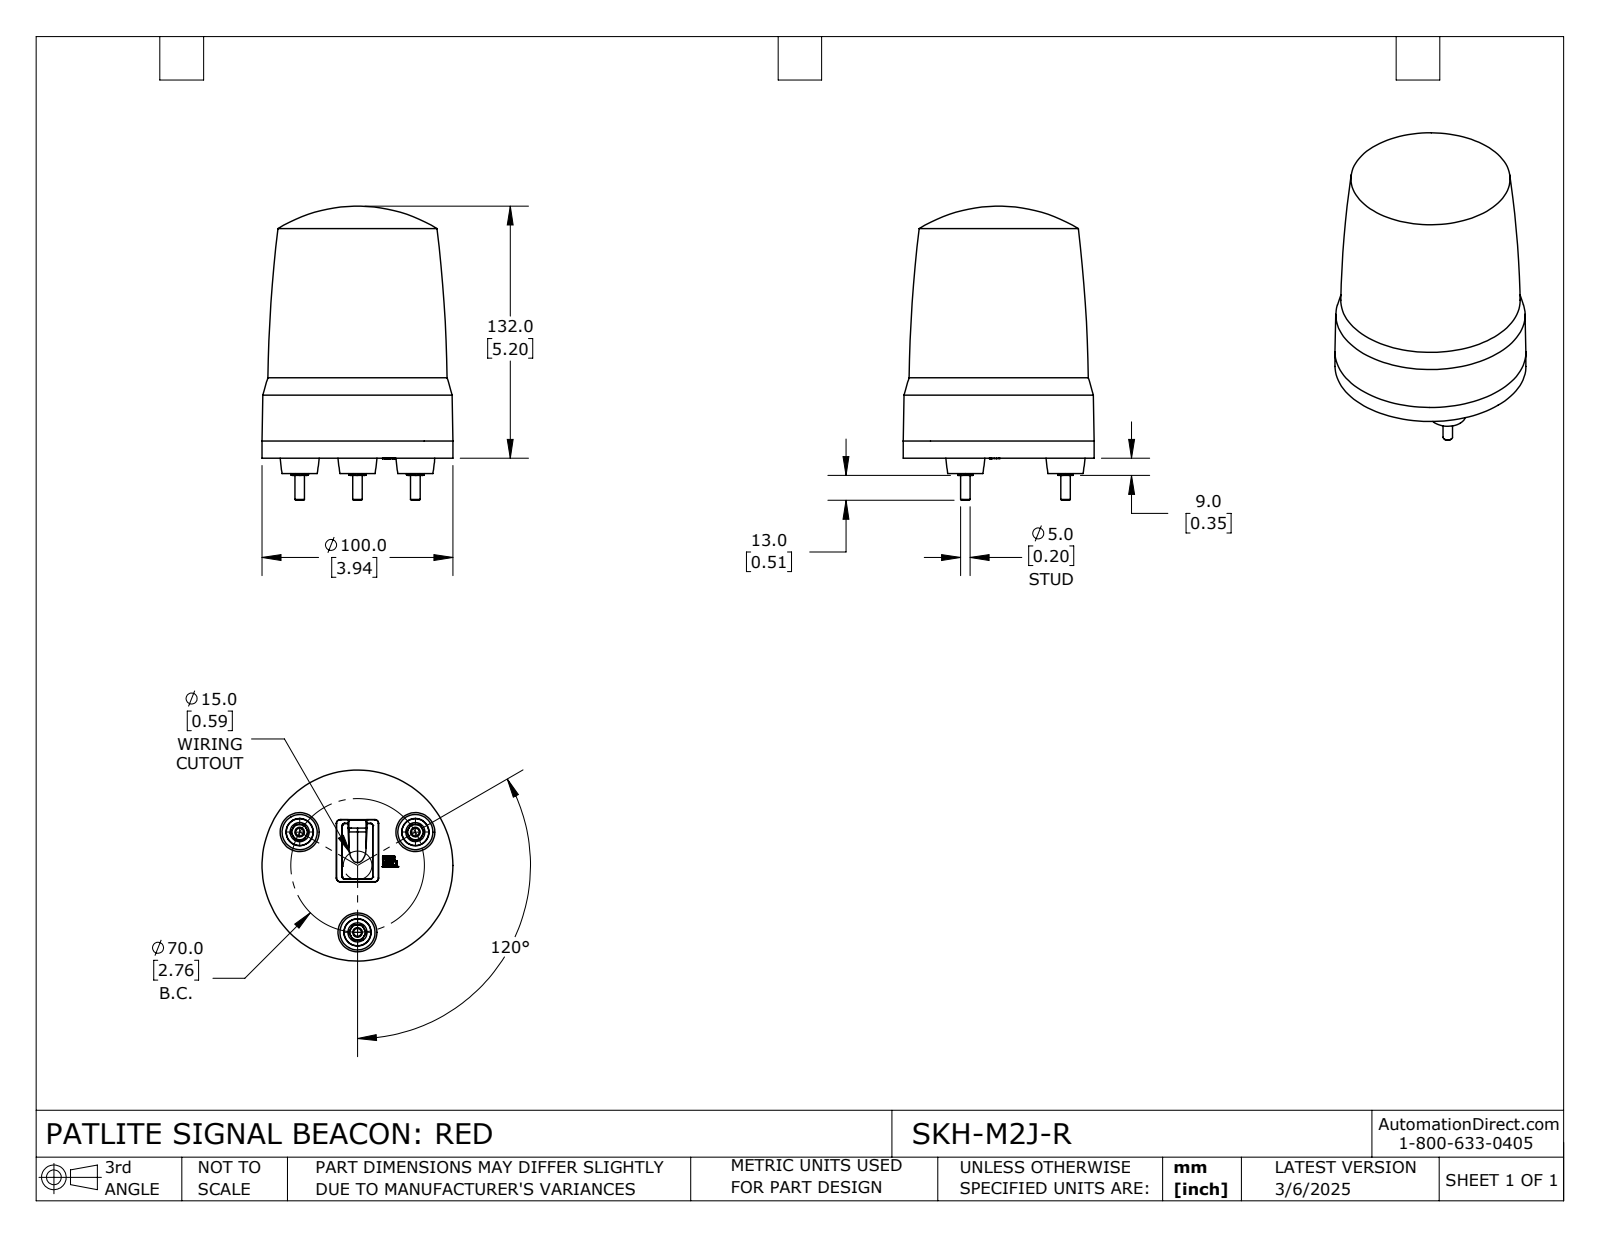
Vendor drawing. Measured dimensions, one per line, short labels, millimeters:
name: SKH-M2J-R
written by: SolidWorks 2024 (CONFIG_CONTROL_DESIGN)
unit: mm
bodies: 1 solid, 327 faces (159 planar, 14 cylindrical, 154 other)
size: 154 × 100 × 100
volume: 859 960 mm³; area: 52 586 mm²
bosses: 3× ⌀10, 3× ⌀5, 1× ⌀100
face distances: 8, 0.85, 8.85, 1.6, 10.45, 2.45, 3.8, 4.2, 5.05, 6.65
